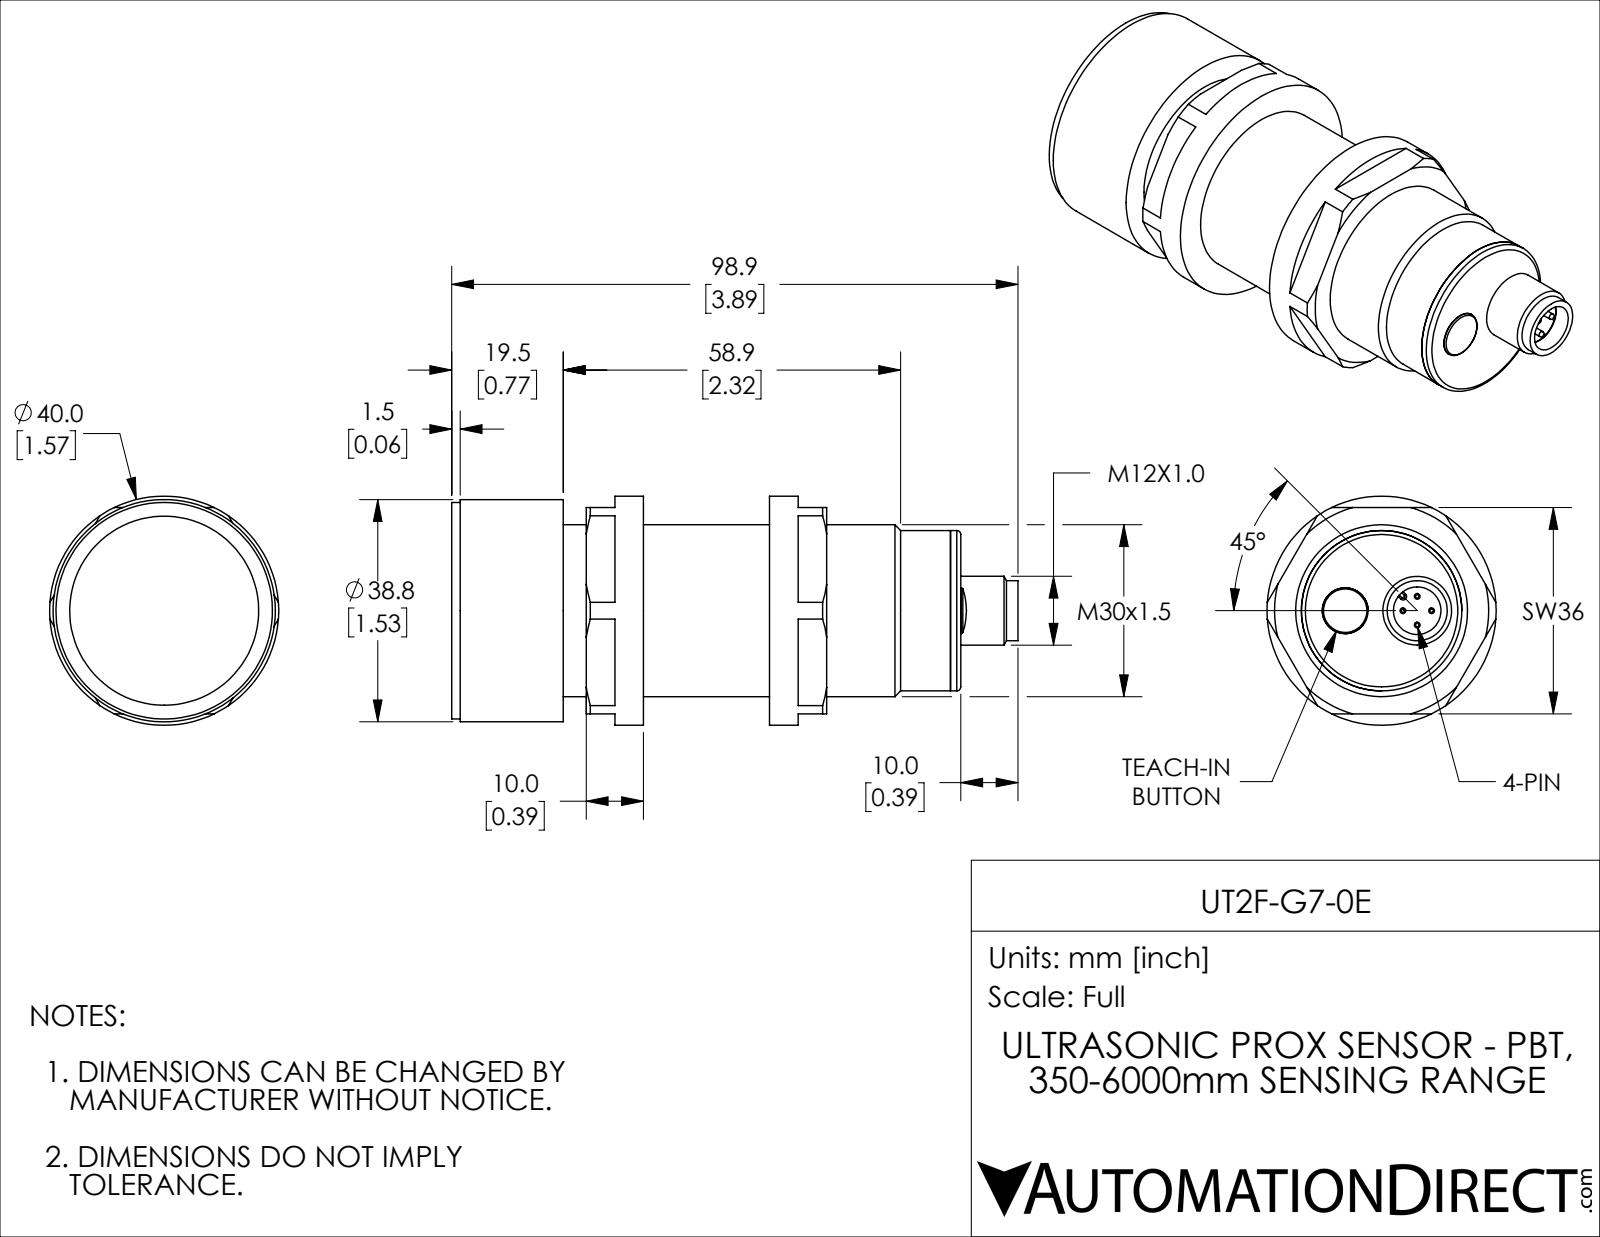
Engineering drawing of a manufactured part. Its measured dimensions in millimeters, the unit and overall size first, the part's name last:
Units: millimetres
Overall size (bounding box): 98.9 × 40 × 40
Round holes (diameter × count): ⌀1.8 ×4, ⌀8 ×1, ⌀8.3 ×1, ⌀9.45 ×1, ⌀30 ×1, ⌀33 ×1
Round bosses / shafts (diameter × count): ⌀1 ×4, ⌀40 ×1, ⌀38.8 ×1, ⌀37.8 ×1, ⌀28 ×1, ⌀12 ×1, ⌀10.5 ×1, ⌀9.25 ×1
Partial cylindrical surfaces — rounded edges, fillets, slot ends (radius × count): R0.3 ×2, R0.6 ×1
Main face-to-face distances: 32, 85.6, 36, 22, 1.49, 87.09, 10, 5, 31.6, 55.49
Hole centre spacings: 2.5, 3.54, 5, 6.7, 12.83, 3.72, 6.22, 6.36
Volume: 81 199 mm³ · Surface area: 22 572 mm²
Bodies: 7 solids, 159 faces (59 planar, 55 cylindrical, 45 other)
Part name (STEP PRODUCT): UT2F-G7-0E
STEP written by: SolidWorks 2018 (AUTOMOTIVE_DESIGN)
